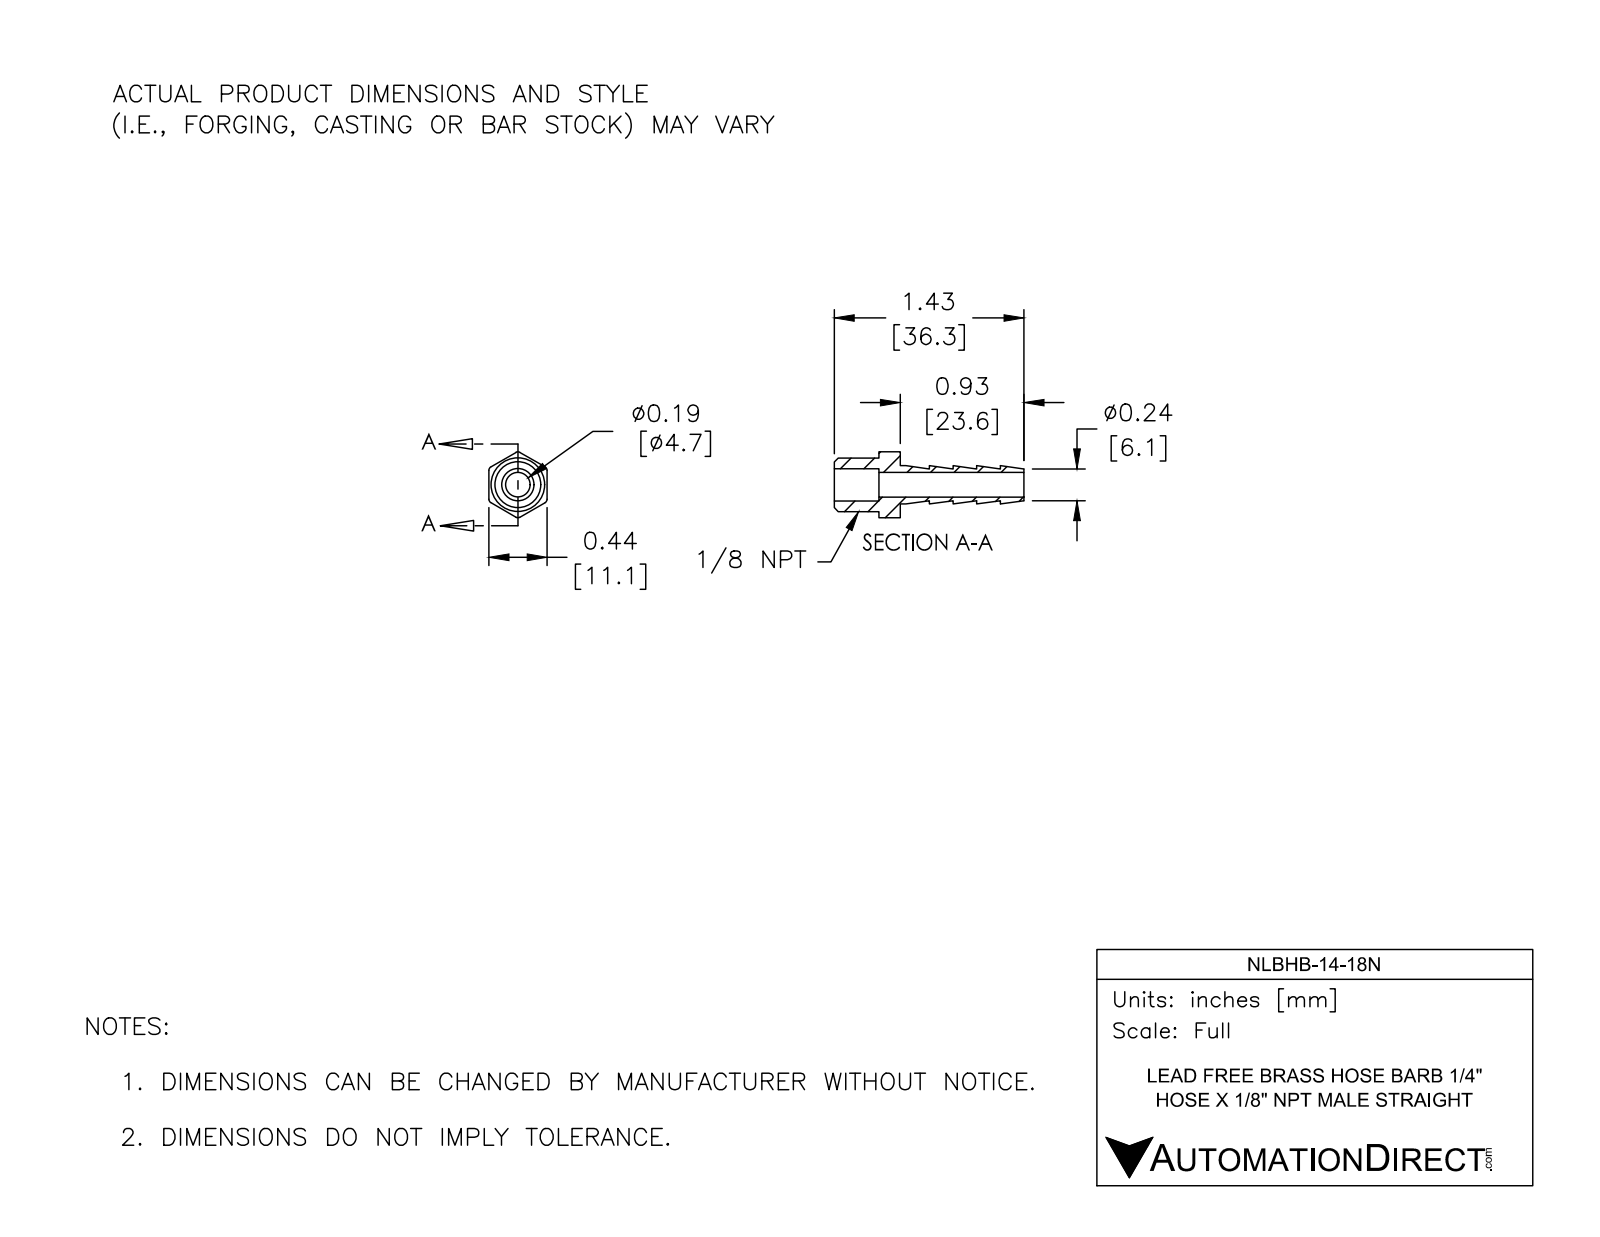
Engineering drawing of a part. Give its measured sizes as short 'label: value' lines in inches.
name: NLBHB-14-18N
written by: SolidWorks 2017 (AUTOMOTIVE_DESIGN)
unit: in
bodies: 1 solid, 41 faces (15 planar, 12 cylindrical, 14 other)
size: 1.428 × 0.496 × 0.438
volume: 0.073 in³; area: 2.635 in²
holes: 1× ⌀0.186, 1× ⌀0.244
bosses: 1× ⌀0.288
rounds: 6× R0.03
face distances: 0.438, 0.178, 0.16, 0.356, 0.497, 0.337, 0.534, 0.753, 0.913, 1.25
